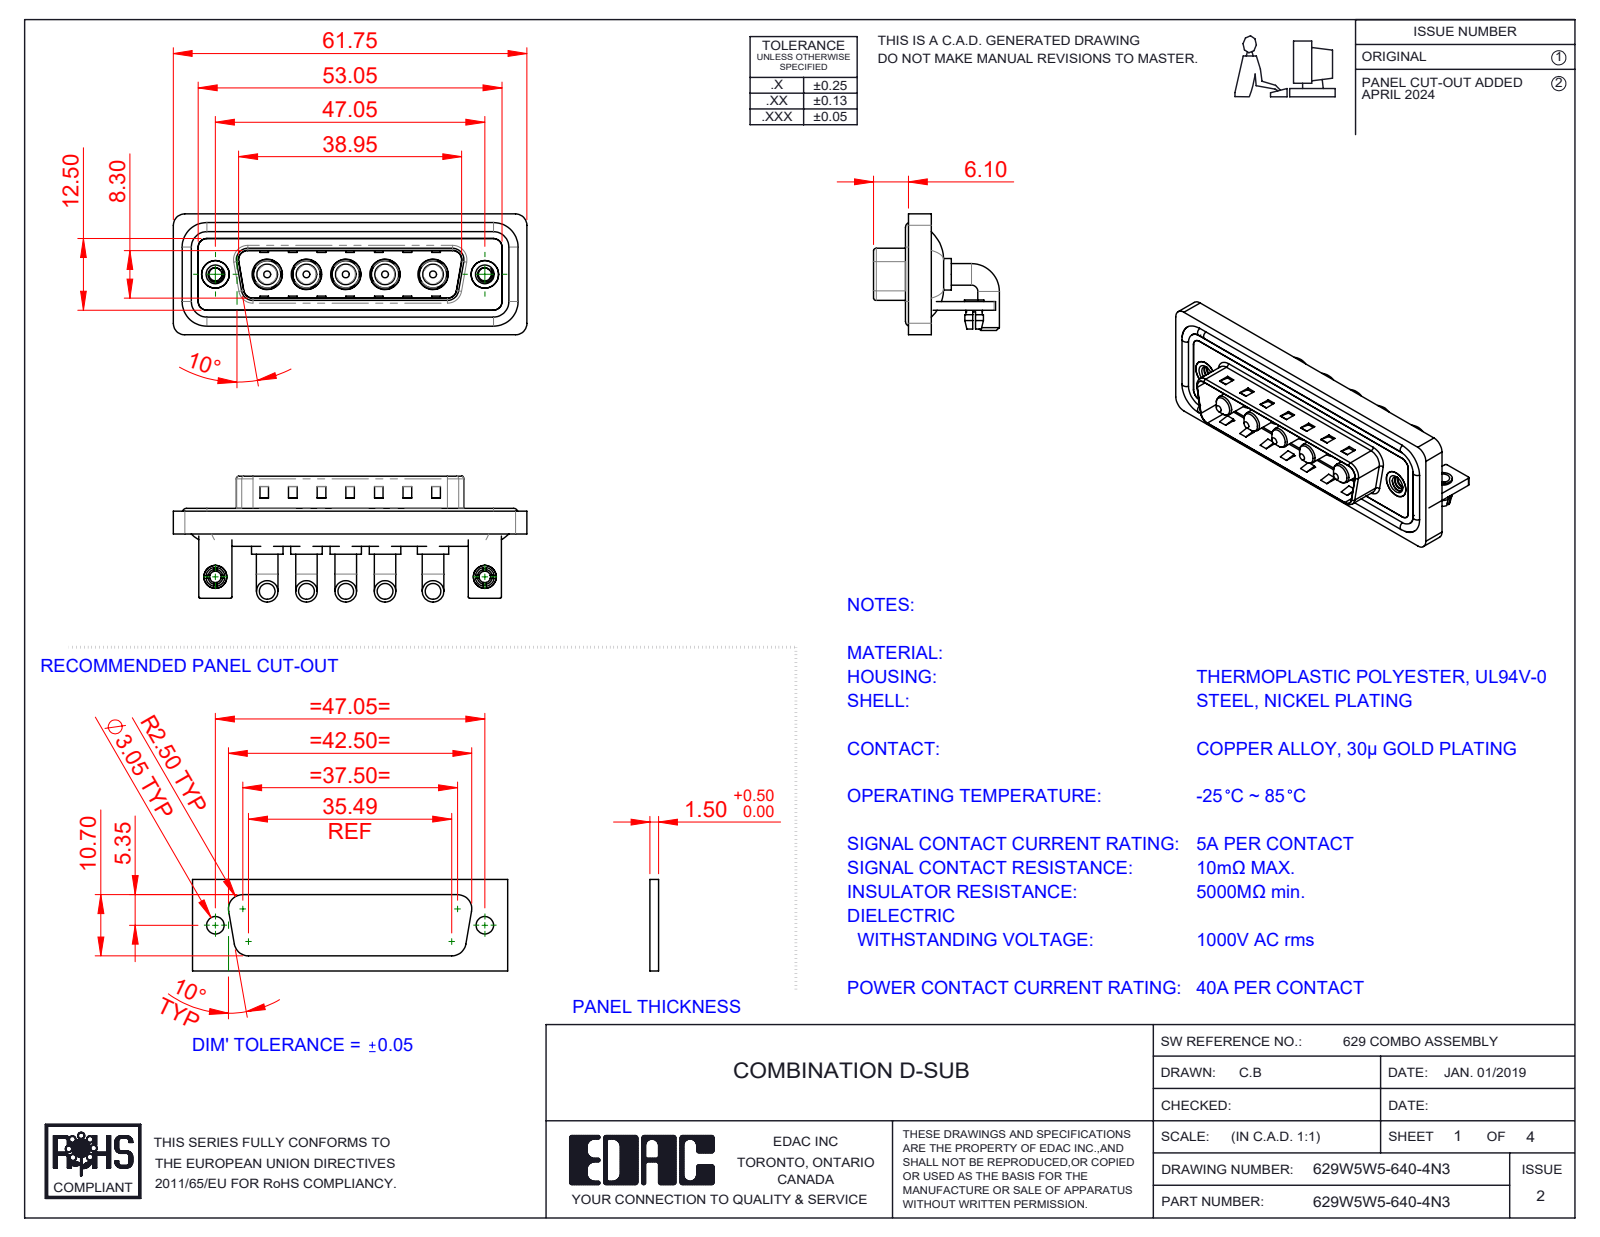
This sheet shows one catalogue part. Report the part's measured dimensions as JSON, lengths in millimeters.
{"part_name": "Power Pin_40A RA; 629Combo Shell Rear_25 Contacts; 629Combo Stabilizer Bracket; 629W5W5-640-4N3 (+5 more)", "step_written_by": "SolidWorks 2023 (CONFIG_CONTROL_DESIGN)", "units": "millimeters", "bodies": {"solids": 21, "faces": 830, "planar": 327, "cylindrical": 343, "other": 160}, "overall_size": [61.75, 21.98, 21.1], "volume_mm3": 8480, "surface_area_mm2": 13289, "round_holes": [[4.85, 5], [5.3, 5], [2, 2], [2.26, 2], [2.5, 2], [3.2, 2], [4, 2], [4.8, 2], [5, 2]], "round_bosses_or_shafts": [[3.75, 10], [5.5, 5], [5.2, 5], [4.75, 5], [3.6, 5], [1.6, 4], [4.9, 2], [4, 2]], "partial_cylinders_radius": [[2, 19], [1.5, 18], [0.25, 16], [0.5, 9], [1.6, 8], [2.1, 5], [0.6, 4], [0.65, 4]], "face_to_face_distances": [0.4, 1.5, 2.9, 0.8, 2.1, 1.1, 3.7, 4.5, 4.1, 1.2], "hole_center_spacings": [6.86, 13.73, 47.05, 6.85, 6.87, 8.37, 8.38, 9.04]}
